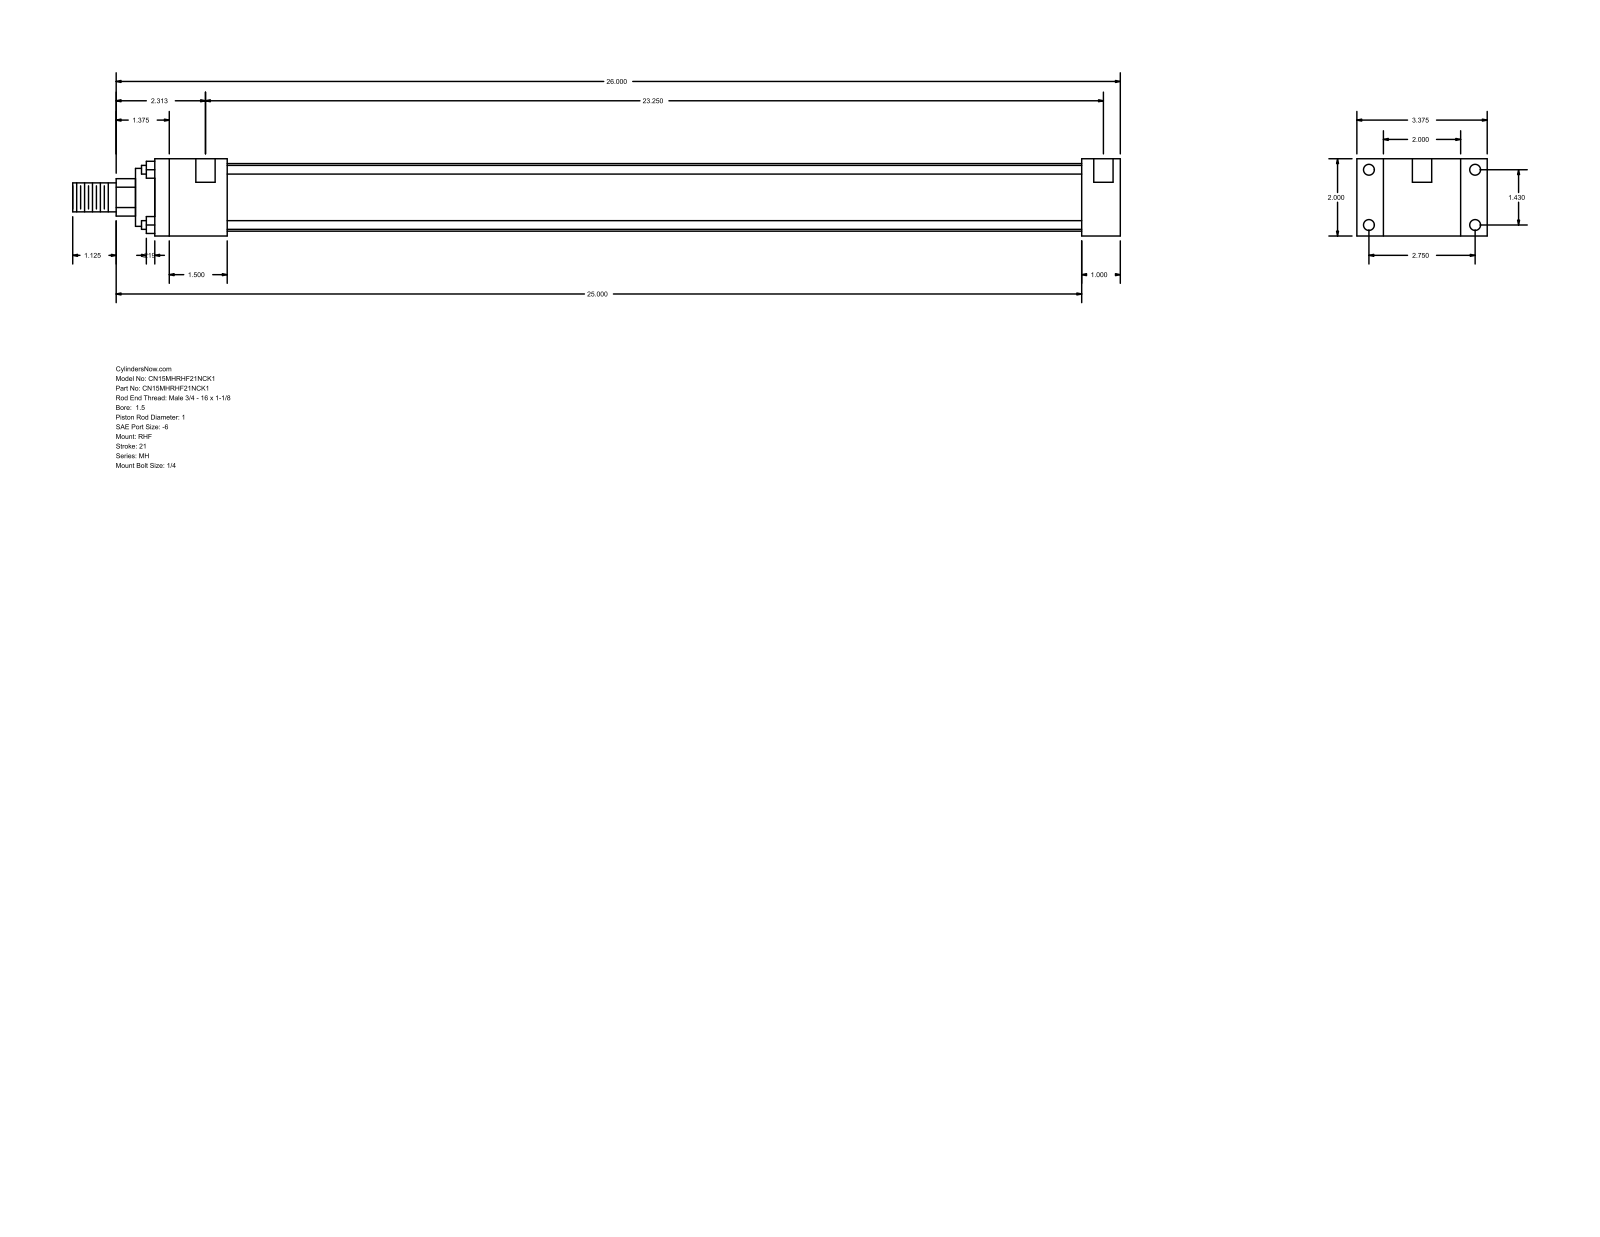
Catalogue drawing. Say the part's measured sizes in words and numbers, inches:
The part is named "MH_RHF__0150_1". Its 3-D file was written by "GSSL Pune (CONFIG_CONTROL_DESIGN)". It is 0 solids with 88 faces: 60 planar, 28 cylindrical and 0 other. Overall it measures 27.125 by 3.375 by 2 inches. Round holes: 4 of diameter 0.219, 4 of diameter 0.281, 2 of diameter 0.5. Round bosses or shafts: 4 of diameter 0.225, 1 of diameter 1.75, 1 of diameter 1.5, 1 of diameter 1, 1 of diameter 0.75. Partial cylindrical surfaces (rounded edges, fillets, slot ends): 1 of radius 0.484. The main face-to-face distances are 2, 1, 0.687, 2.687, 3.375, 25, 24, 1.875, 22.125, 23.125. The hole center spacings are 1.43, 2.75, 3.099, 23.375, 0.125, 23.25.
